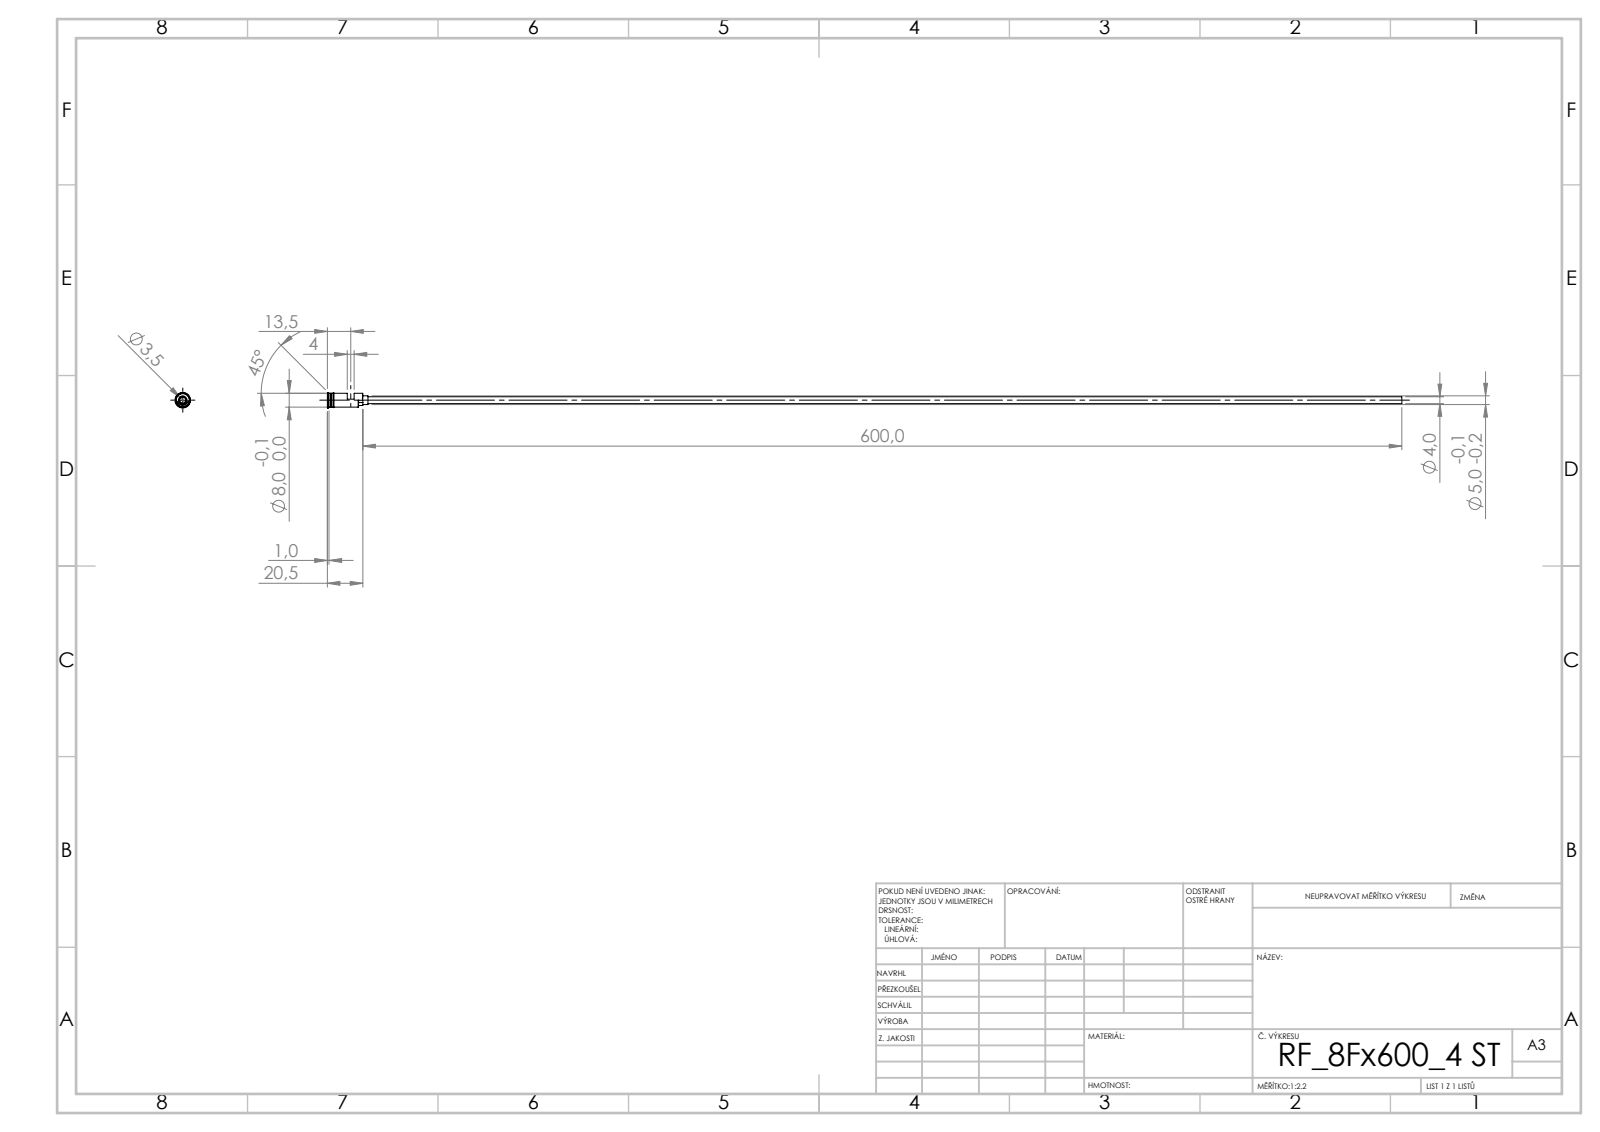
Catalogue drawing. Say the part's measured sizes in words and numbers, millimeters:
Its 3-D file was written by "SolidWorks 2019 (CONFIG_CONTROL_DESIGN)". It is 1 solid with 55 faces: 24 planar, 19 cylindrical and 12 other. Overall it measures 620.5 by 9 by 9 millimeters. Its volume is 2 622 cubic millimeters and its surface area 14 906 square millimeters. Round holes: 1 of diameter 3.5. Round bosses or shafts: 1 of diameter 9, 1 of diameter 8, 1 of diameter 7.8, 1 of diameter 5, 1 of diameter 4. Partial cylindrical surfaces (rounded edges, fillets, slot ends): 2 of radius 3, 1 of radius 3.05. The main face-to-face distances are 4, 11.5, 9, 20.5, 5, 15.5, 2.5, 18.5, 13.5, 9.5.
